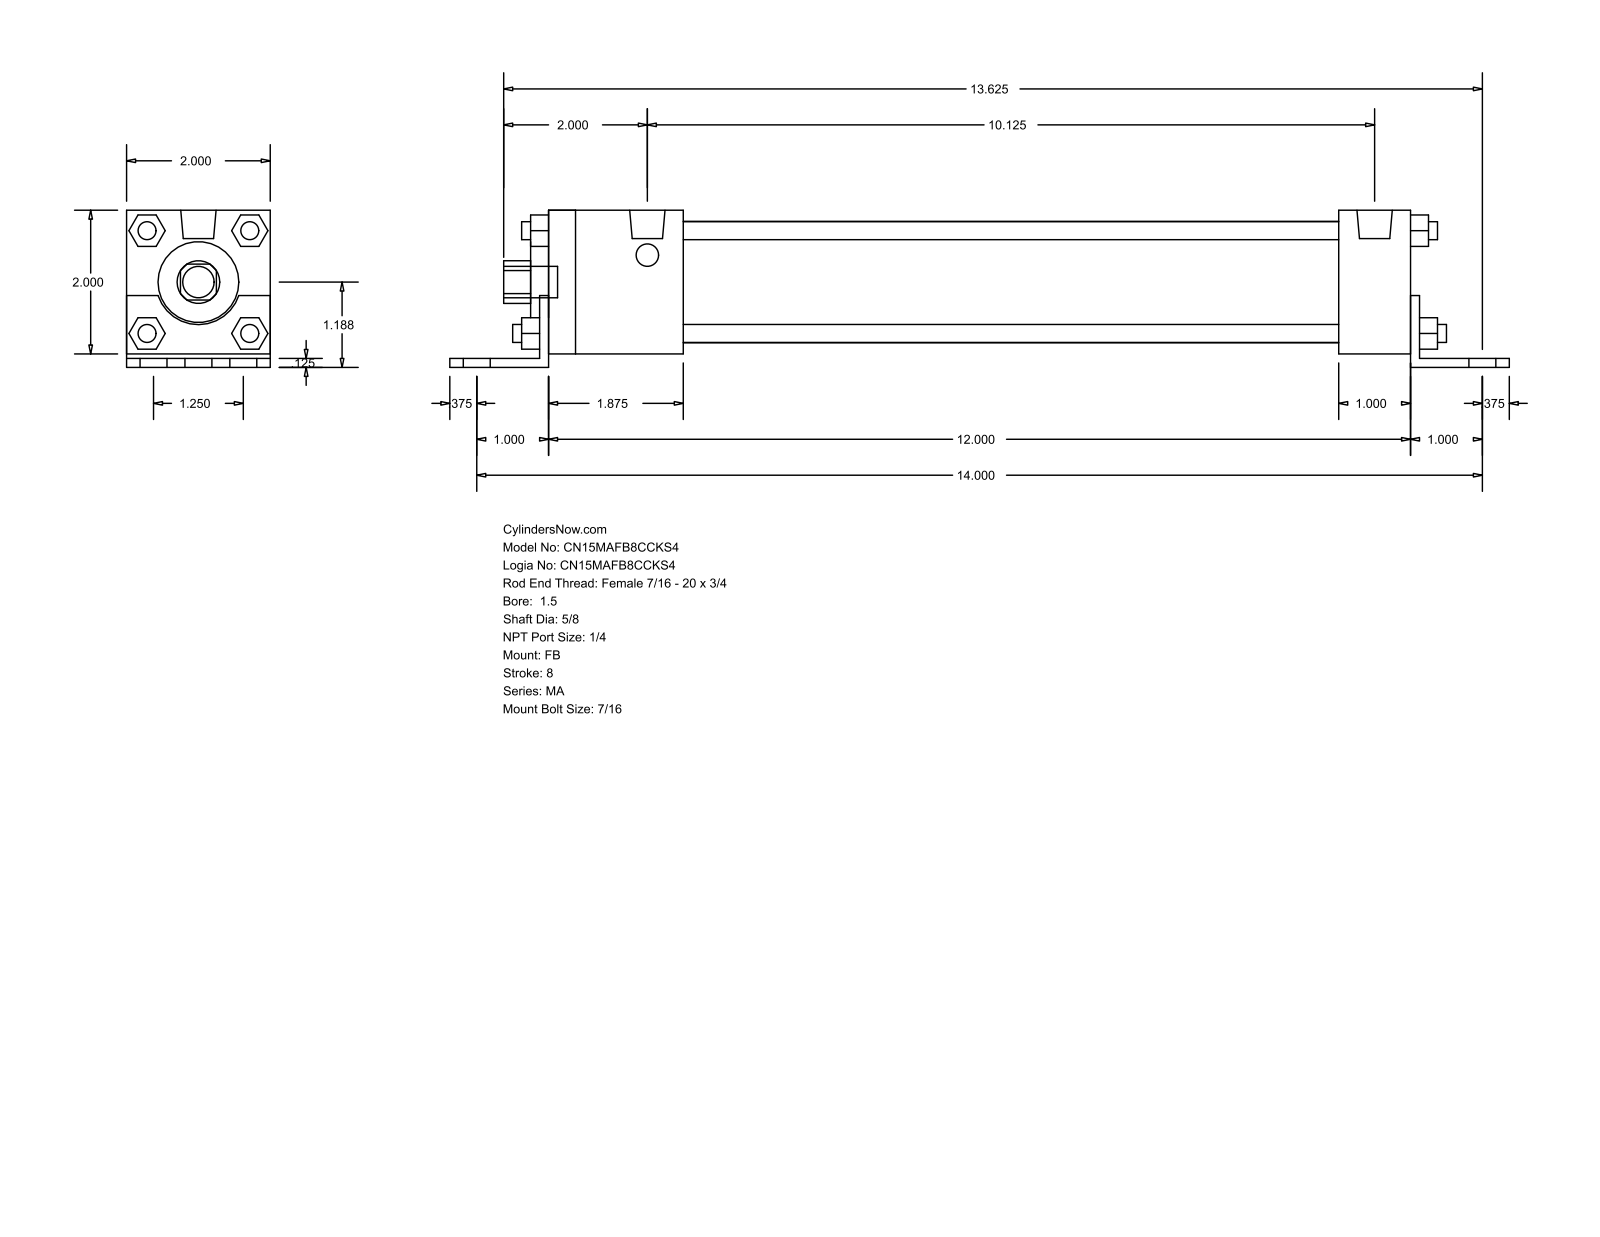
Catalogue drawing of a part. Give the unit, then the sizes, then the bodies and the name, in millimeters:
Units: millimetres
Overall size (bounding box): 374.65 × 55.56 × 50.8
Round holes (diameter × count): ⌀15.88 ×1, ⌀28.57 ×1, ⌀42.93 ×1
Round bosses / shafts (diameter × count): ⌀11.11 ×7, ⌀7.94 ×4, ⌀6.35 ×4, ⌀12.49 ×2
Partial cylindrical surfaces — rounded edges, fillets, slot ends (radius × count): R7.54 ×1, R15.05 ×1
Main face-to-face distances: 50.8, 3.17, 4.76, 55.56, 1.59, 52.39, 311.15, 3.18, 304.8, 28.58
Bodies: 0 solids, 140 faces (105 planar, 35 cylindrical, 0 other)
Part name (STEP PRODUCT): MA_FB__0150_0.625
STEP written by: GSSL Pune (CONFIG_CONTROL_DESIGN)
